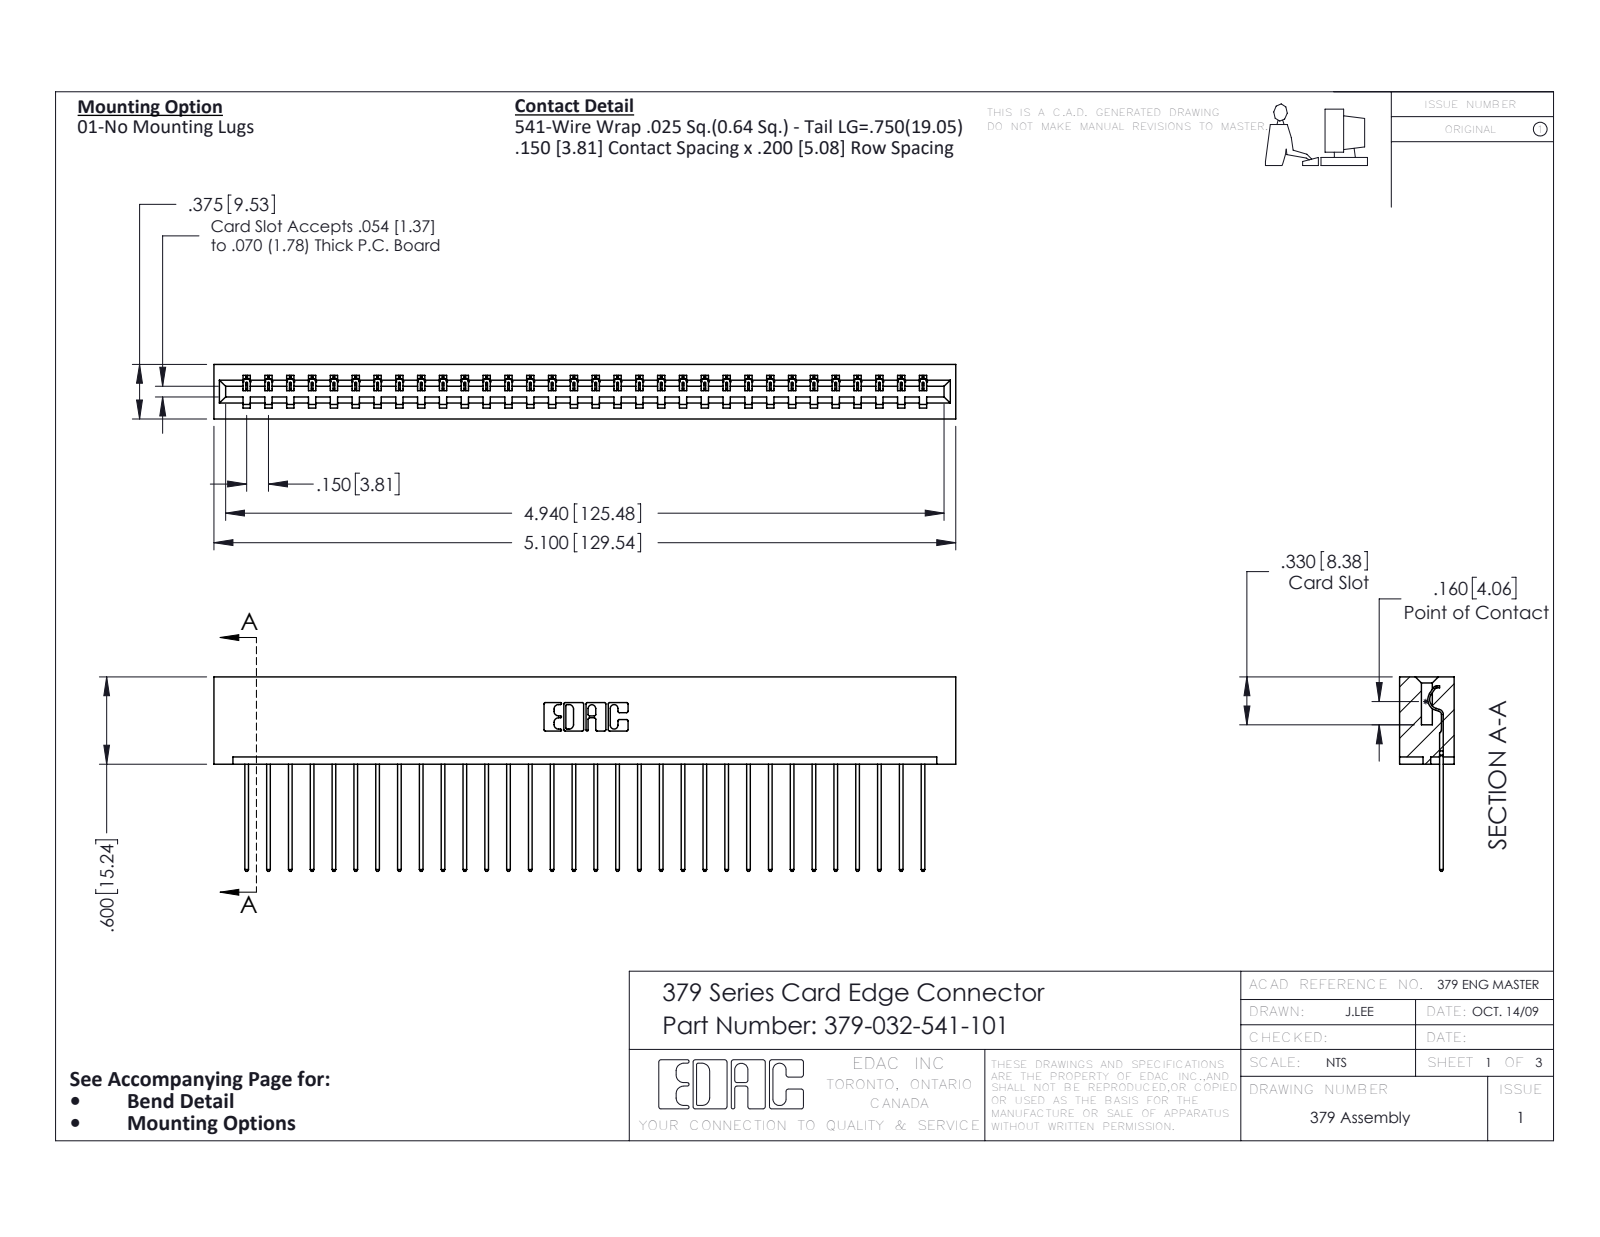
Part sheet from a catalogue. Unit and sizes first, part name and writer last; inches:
Units: inches
Overall size (bounding box): 5.1 × 1.337 × 0.375
Partial cylindrical surfaces — rounded edges, fillets, slot ends (radius × count): R0.006 ×64, R0.01 ×64, R0.01 ×22, R0.007 ×6, R0.031 ×6, R0.026 ×3, R0.014 ×1, R0.022 ×1
Main face-to-face distances: 0.3, 0.075, 0.375, 0.225, 0.1, 0.275, 0.025, 0.6, 0.2, 0.15
Volume: 0.874 in³ · Surface area: 23.58 in²
Bodies: 33 solids, 1962 faces (1410 planar, 552 cylindrical, 0 other)
Part name (STEP PRODUCT): 345-292-001_345-293-141; 379-032-541-101; 379 Part_Lugless
STEP written by: SolidWorks 2016 (CONFIG_CONTROL_DESIGN)
